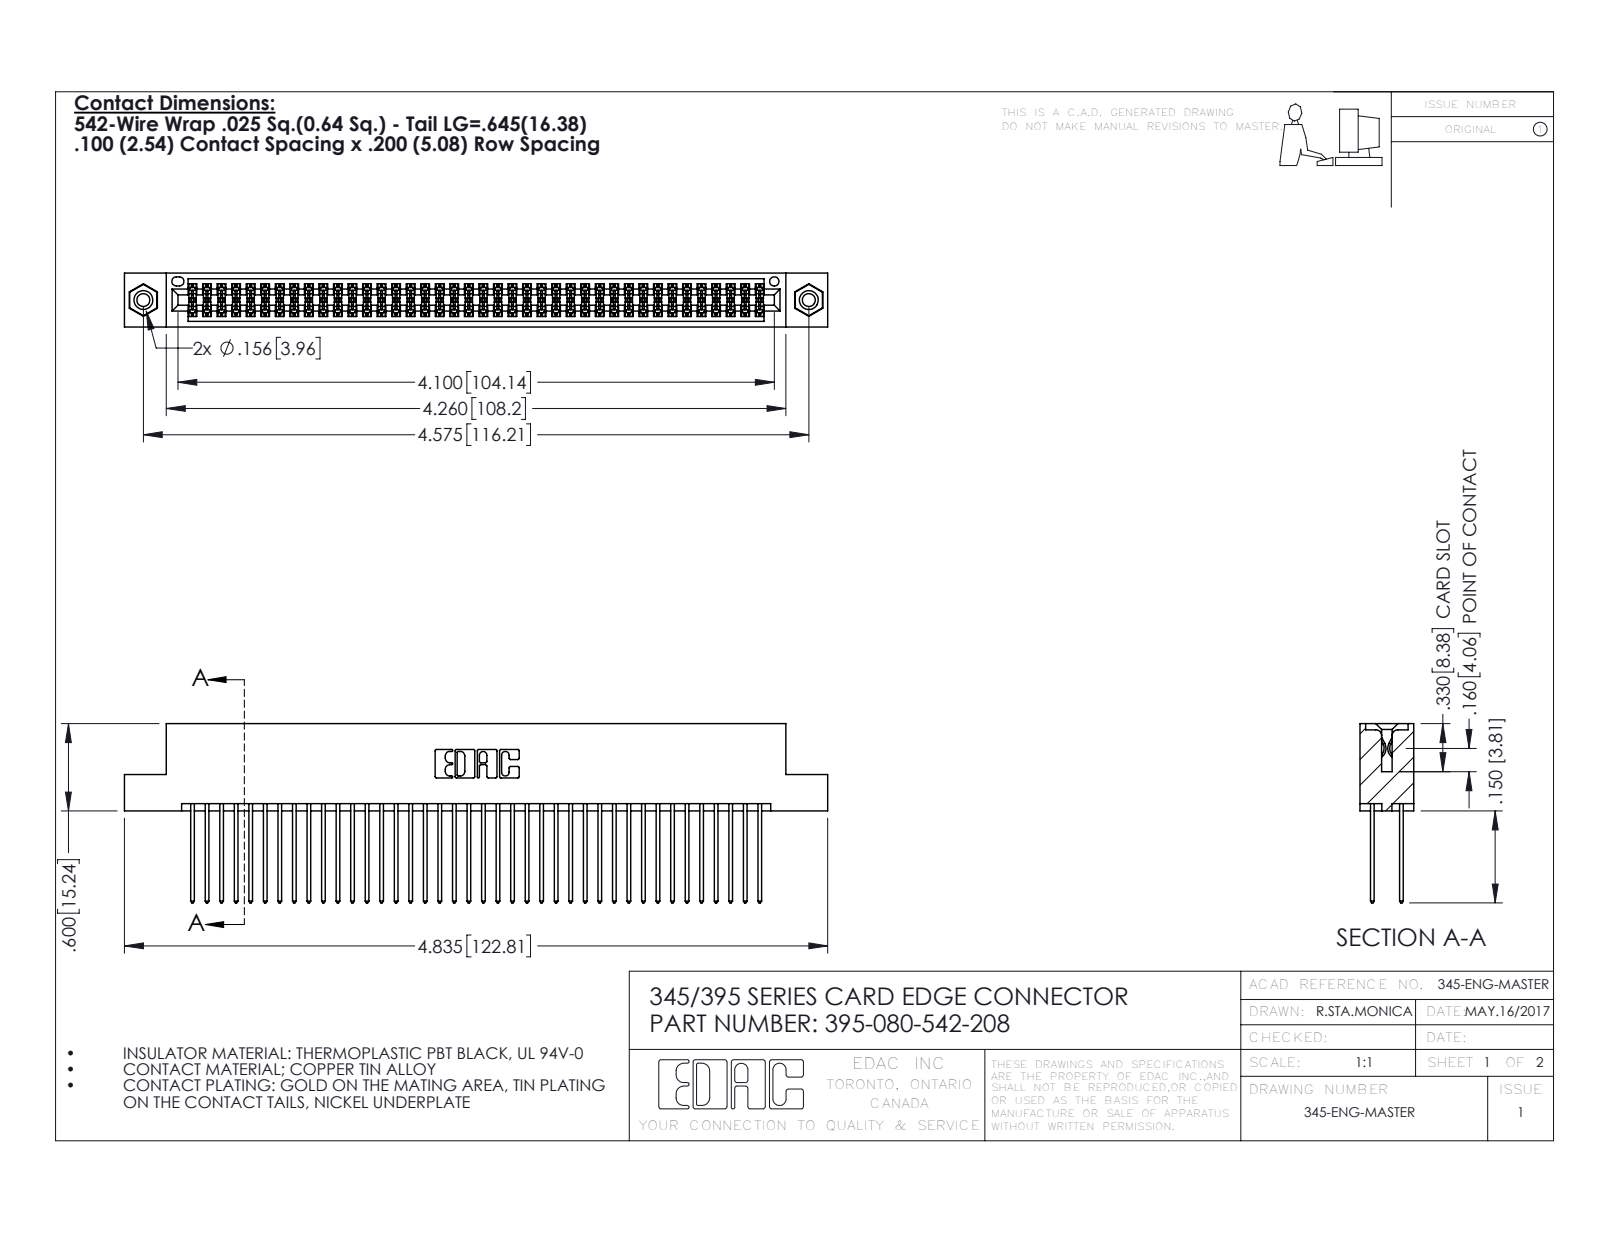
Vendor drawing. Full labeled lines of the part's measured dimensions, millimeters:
Part name (STEP PRODUCT): 345-250-001_345-250-003-102; 345 Part_Flush Mounting Lugs - 0.156 Dia-TI; 345-292-001_345-293-142; 395-080-542-208
STEP written by: SolidWorks 2016 (CONFIG_CONTROL_DESIGN)
Units: millimetres
Bodies: 83 solids, 4186 faces (2752 planar, 1418 cylindrical, 16 other)
Overall size (bounding box): 122.8 × 31.3 × 9.4
Volume: 12 300 mm³ · Surface area: 19 860 mm²
Round holes (diameter × count): ⌀2.3 ×2, ⌀3.2 ×2, ⌀4 ×2, ⌀1.6 ×1
Round bosses / shafts (diameter × count): ⌀3.9 ×2
Partial cylindrical surfaces — rounded edges, fillets, slot ends (radius × count): R0.2 ×120, R0.3 ×80, R0.3 ×22, R0.2 ×6, R0.8 ×6, R0.7 ×3, R0.4 ×2, R0.5 ×2
Main face-to-face distances: 1.8, 7.6, 5.1, 2.5, 6.9, 0.6, 9.4, 5.7, 4.4, 3.8
Hole centre spacings: 6.9, 110.2, 116.2
